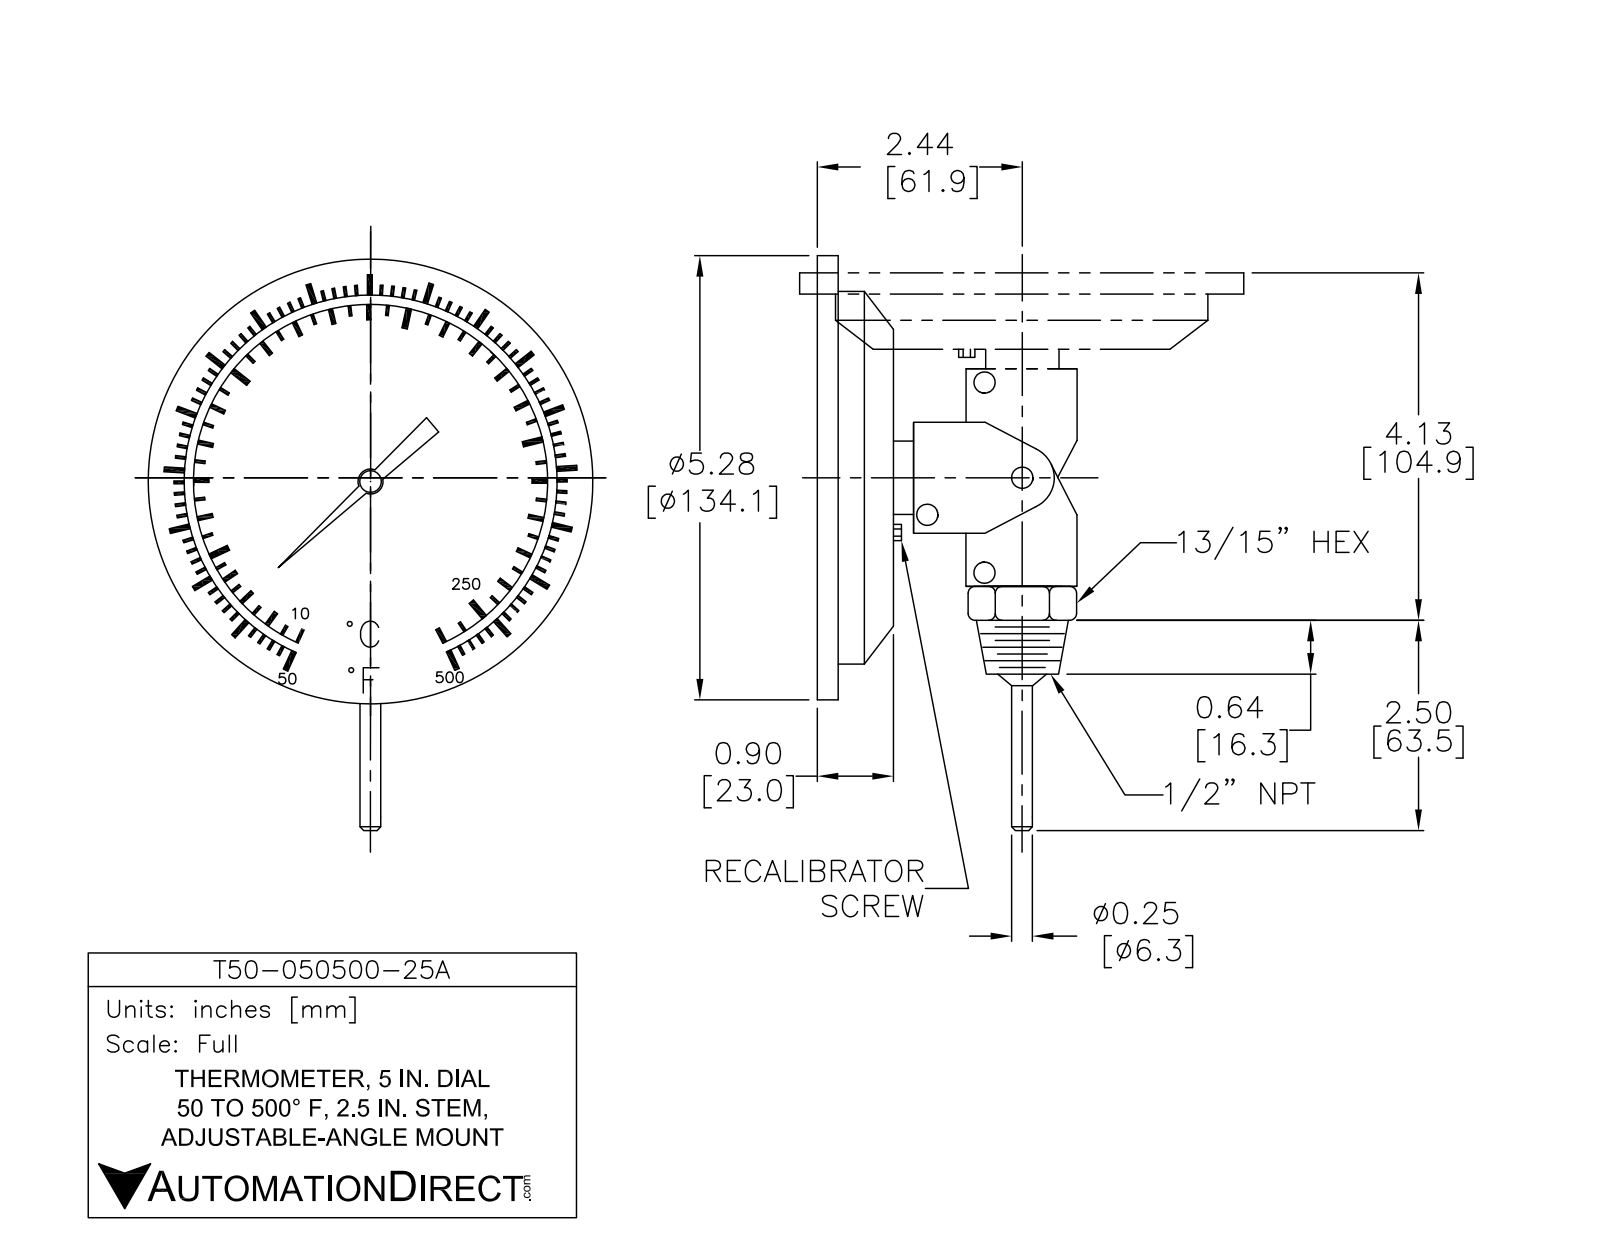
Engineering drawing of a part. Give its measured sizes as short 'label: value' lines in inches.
name: T50-50500-25A
written by: SolidWorks 2021 (AUTOMOTIVE_DESIGN)
unit: in
bodies: 1 solid, 507 faces (281 planar, 45 cylindrical, 181 other)
size: 6.46 × 5.28 × 5.28
volume: 10.06 in³; area: 95.62 in²
holes: 1× ⌀3.424, 1× ⌀3.706, 1× ⌀4.76, 1× ⌀4.836
bosses: 4× ⌀0.305, 2× ⌀0.145, 1× ⌀5.28, 1× ⌀4.97, 1× ⌀3.454, 1× ⌀0.85, 1× ⌀0.822, 1× ⌀0.544
rounds: 10× R0.06, 4× R0.04, 1× R0.17, 1× R0.336, 1× R0.336, 1× R0.342, 1× R0.4, 1× R1.868
face distances: 0.353, 0.074, 0.055, 0.427, 1.19, 0.815, 0.462, 0.388, 1.245, 2.435
